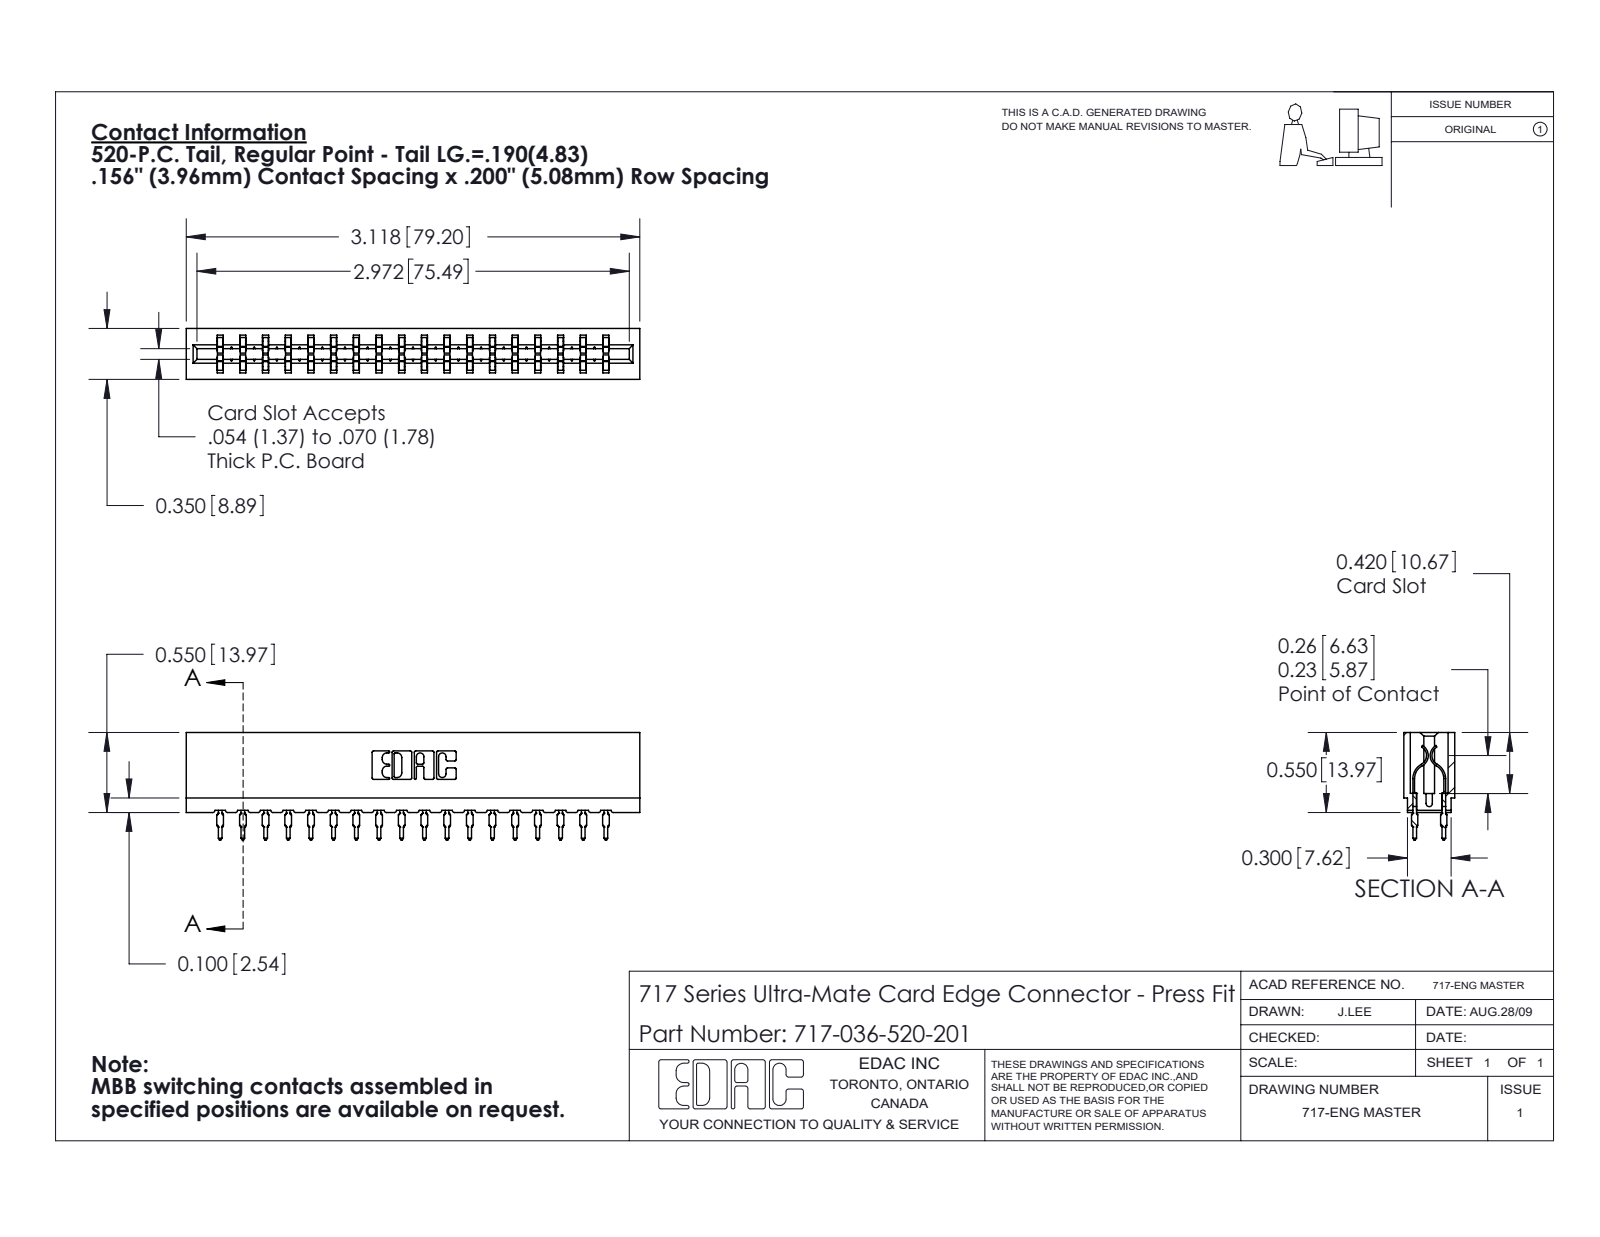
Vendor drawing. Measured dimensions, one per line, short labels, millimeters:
name: 717 Part_Insulator Option - 06; 745-292-001_520; 717-036-520-201
written by: SolidWorks 2020 (CONFIG_CONTROL_DESIGN)
unit: mm
bodies: 37 solids, 3334 faces (1728 planar, 670 cylindrical, 936 other)
size: 79.2 × 18.8 × 8.9
volume: 6 930 mm³; area: 10 100 mm²
rounds: 72× R0.5, 36× R0.4, 22× R0.3, 8× R0.1, 8× R0.3, 6× R0.2, 6× R0.8, 3× R0.7
face distances: 5.4, 3.5, 8.9, 4, 15.8, 1.9, 1.6, 7.3, 1.9, 3.8
